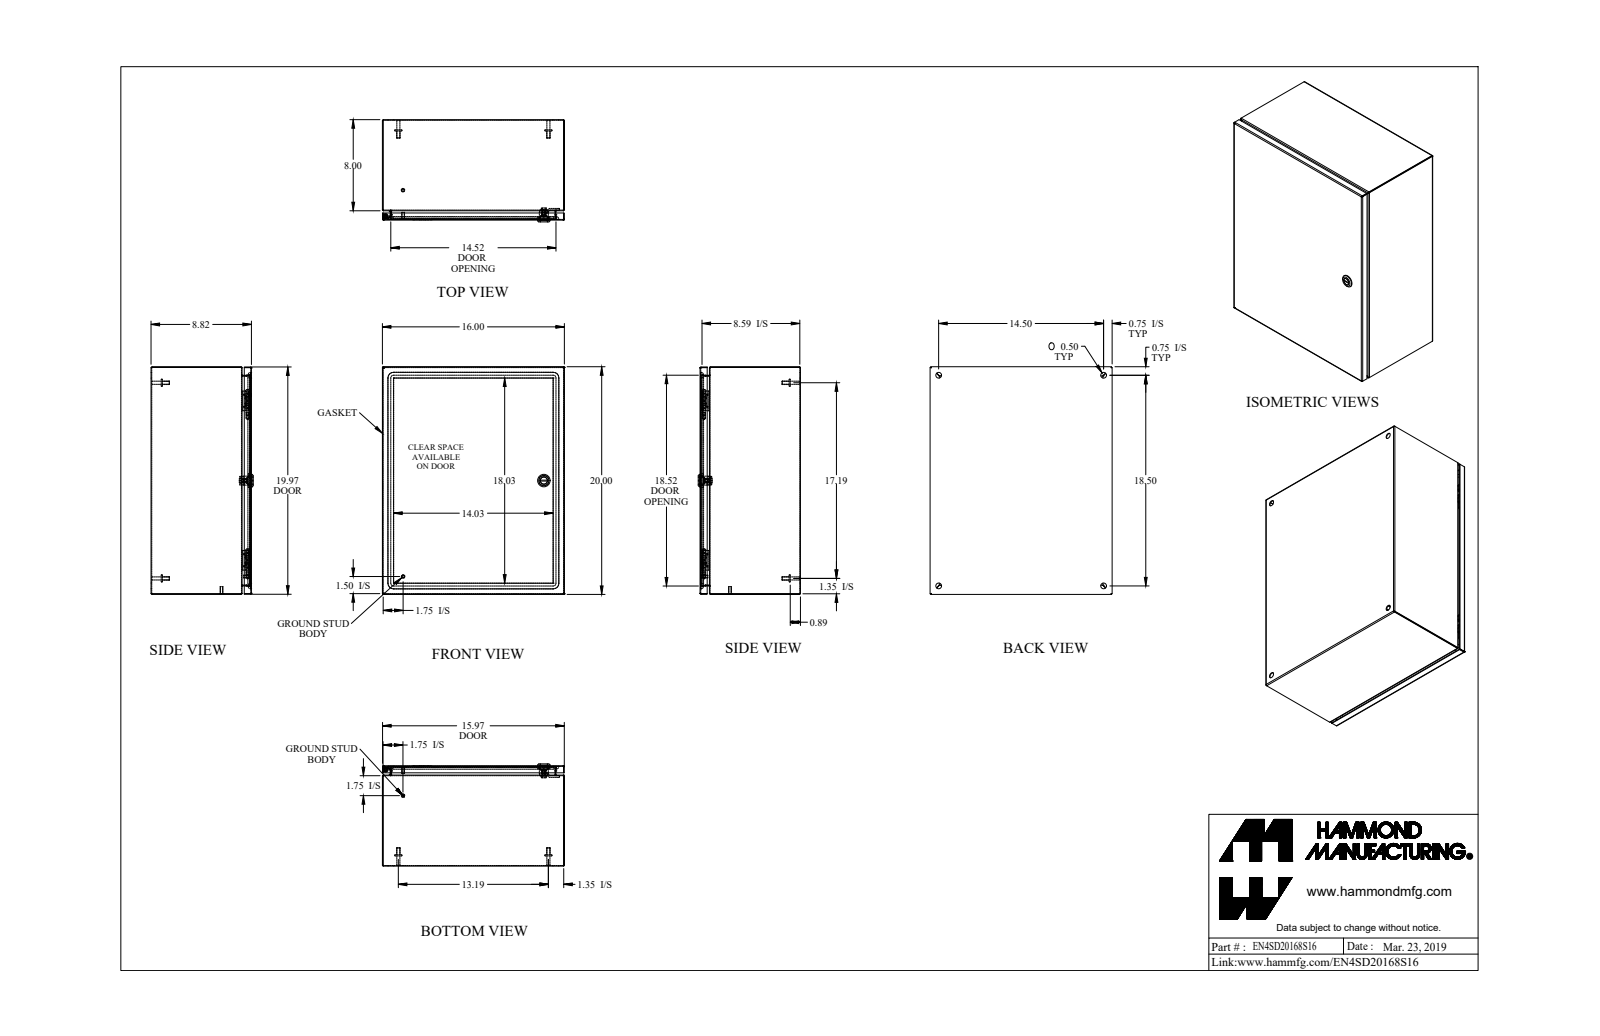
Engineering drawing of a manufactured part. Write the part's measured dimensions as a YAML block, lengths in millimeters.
part_name: "EN4SD20168S16_Default"
step_written_by: "SolidWorks 2019 (CONFIG_CONTROL_DESIGN)"
units: millimeters
bodies: {solids: 22, faces: 656, planar: 303, cylindrical: 211, other: 142}
overall_size: [508, 406.4, 228.1]
volume: 1384000
surface_area: 1855000
round_holes:
  - {diameter: 12.7, count: 5}
  - {diameter: 4.4, count: 1}
  - {diameter: 5, count: 1}
  - {diameter: 6.1, count: 1}
  - {diameter: 6.1, count: 1}
  - {diameter: 9.8, count: 1}
  - {diameter: 16, count: 1}
  - {diameter: 19.5, count: 1}
round_bosses_or_shafts:
  - {diameter: 8, count: 6}
  - {diameter: 15.9, count: 4}
  - {diameter: 7, count: 4}
  - {diameter: 6.4, count: 2}
  - {diameter: 27.9, count: 1}
  - {diameter: 19.9, count: 1}
  - {diameter: 15.9, count: 1}
  - {diameter: 13.3, count: 1}
partial_cylinders:
  - {radius: 0.7, count: 21}
  - {radius: 2.2, count: 21}
  - {radius: 4.8, count: 12}
  - {radius: 0.2, count: 4}
  - {radius: 1.6, count: 4}
  - {radius: 6.4, count: 4}
  - {radius: 12.7, count: 4}
  - {radius: 3.2, count: 2}
face_to_face_distances: [1.4, 1.4, 221.2, 222.6, 222.6, 224.1, 405, 506.6, 403.5, 406.4]
hole_center_spacings: [236.5, 368.3, 414.4, 469.9, 597.1]
